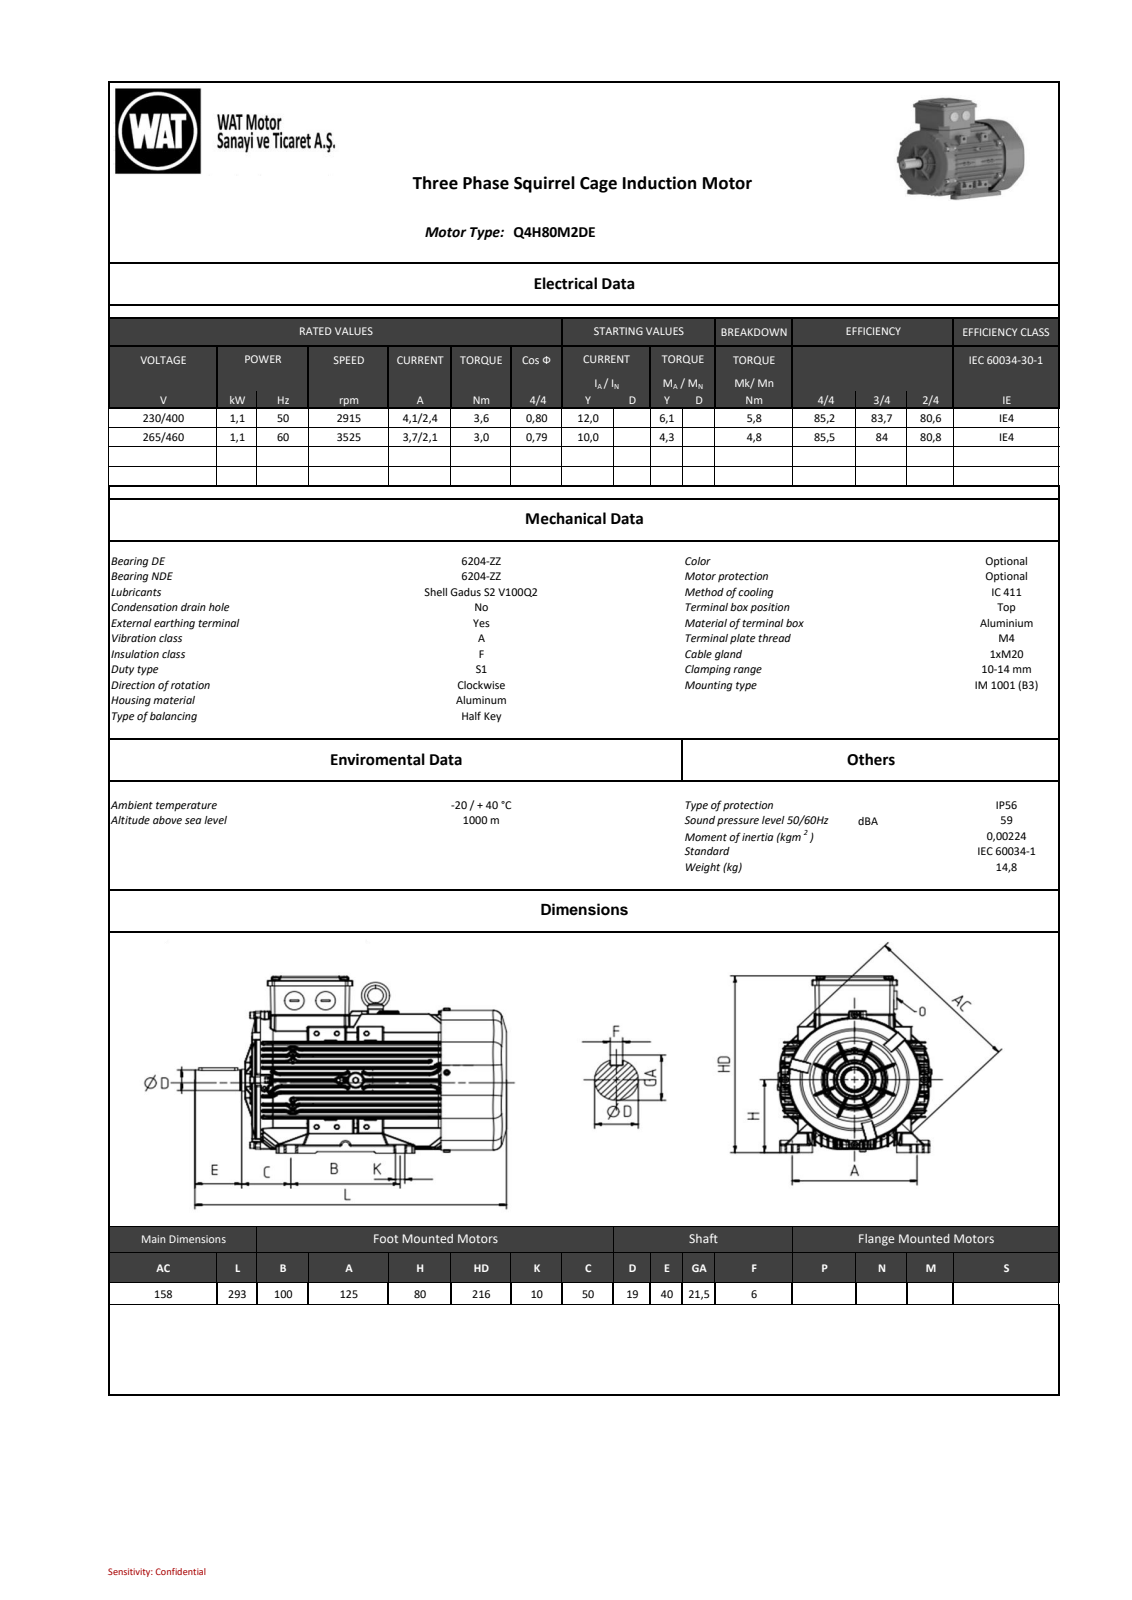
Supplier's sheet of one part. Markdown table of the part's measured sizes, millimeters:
| quantity | value |
| --- | --- |
| part name | model1 |
| STEP written by | SIEMENS PLM Software NX2206.8101 (AUTOMOTIVE_DESIGN) |
| units | millimeters |
| bodies | 0 solids, 6416 faces (1287 planar, 1929 cylindrical, 3200 other) |
| overall size | 293 × 215.5 × 158 |
| round holes (diameter × count) | 3 × 3, 3.5 × 2, 4.6 × 2, 5 × 2, 3.3 × 1, 8 × 1, 57 × 1 |
| round bosses / shafts (diameter × count) | 6 × 5, 8.33 × 3, 21.38 × 2, 146.5 × 1, 61 × 1, 30 × 1, 24.07 × 1, 20.2 × 1 |
| partial cylindrical surfaces (radius × count) | 0.5 × 536, 1 × 360, 0.8 × 323, 2 × 29, 5 × 22, 8 × 8, 3 × 6, 75.75 × 6 |
| main face-to-face distances | 1, 41.96, 157, 10.36, 156.98, 86, 18, 20.98, 10.49, 7 |
| hole center spacings | 25.5, 44.17, 44.16, 50.3, 54.45, 70.94 |
